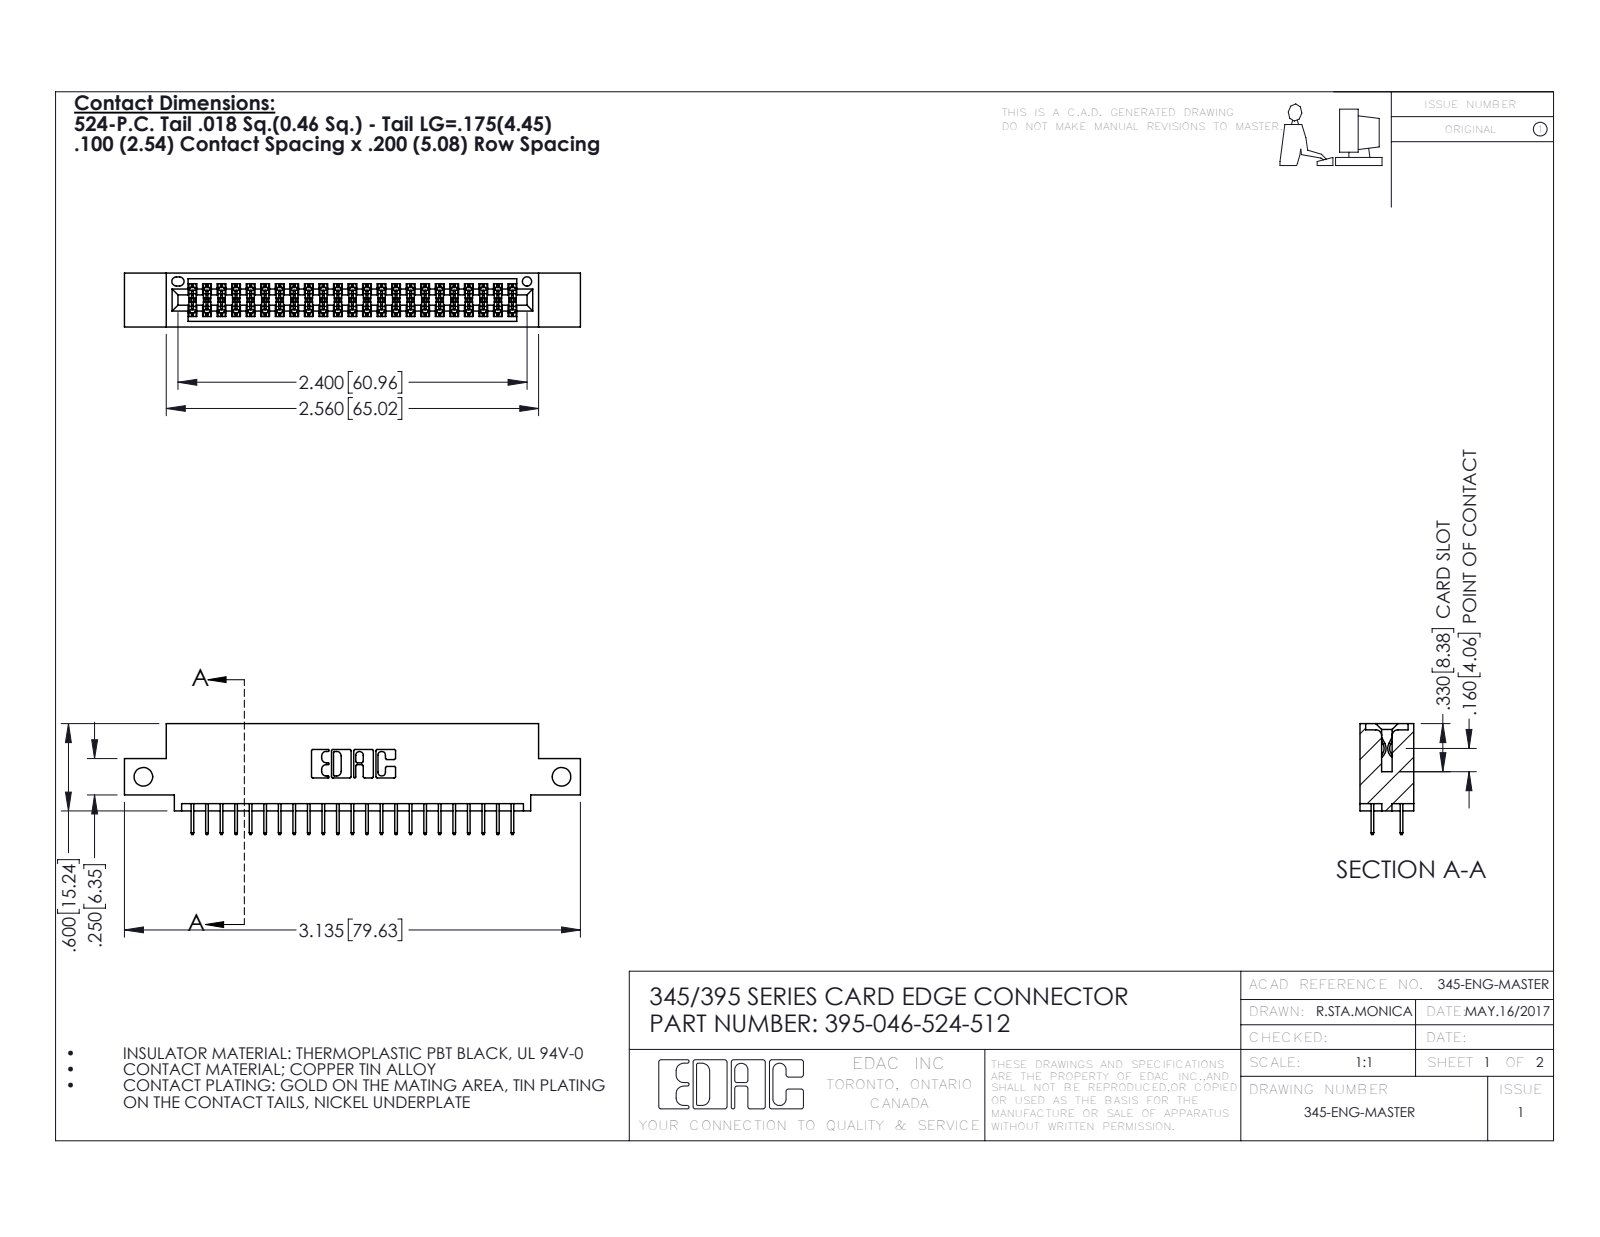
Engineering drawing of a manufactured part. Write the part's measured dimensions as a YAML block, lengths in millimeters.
part_name: "345 Part_0.110 Offset - Side Mount; 395-046-524-512; 345-292-001_345-293-124"
step_written_by: "SolidWorks 2016 (CONFIG_CONTROL_DESIGN)"
units: millimeters
bodies: {solids: 47, faces: 2614, planar: 1878, cylindrical: 736, other: 0}
overall_size: [79.6, 19.4, 9.4]
volume: 7330
surface_area: 10240
round_holes:
  - {diameter: 3.3, count: 2}
  - {diameter: 1.6, count: 1}
partial_cylinders:
  - {radius: 0.2, count: 69}
  - {radius: 0.3, count: 22}
  - {radius: 0.2, count: 6}
  - {radius: 0.8, count: 6}
  - {radius: 0.7, count: 3}
  - {radius: 0.4, count: 2}
  - {radius: 0.5, count: 2}
  - {radius: 0.6, count: 2}
face_to_face_distances: [1.8, 7.6, 5.1, 9.4, 2.5, 6.9, 0.6, 5.7, 1.8, 4.4]
hole_center_spacings: [73]
